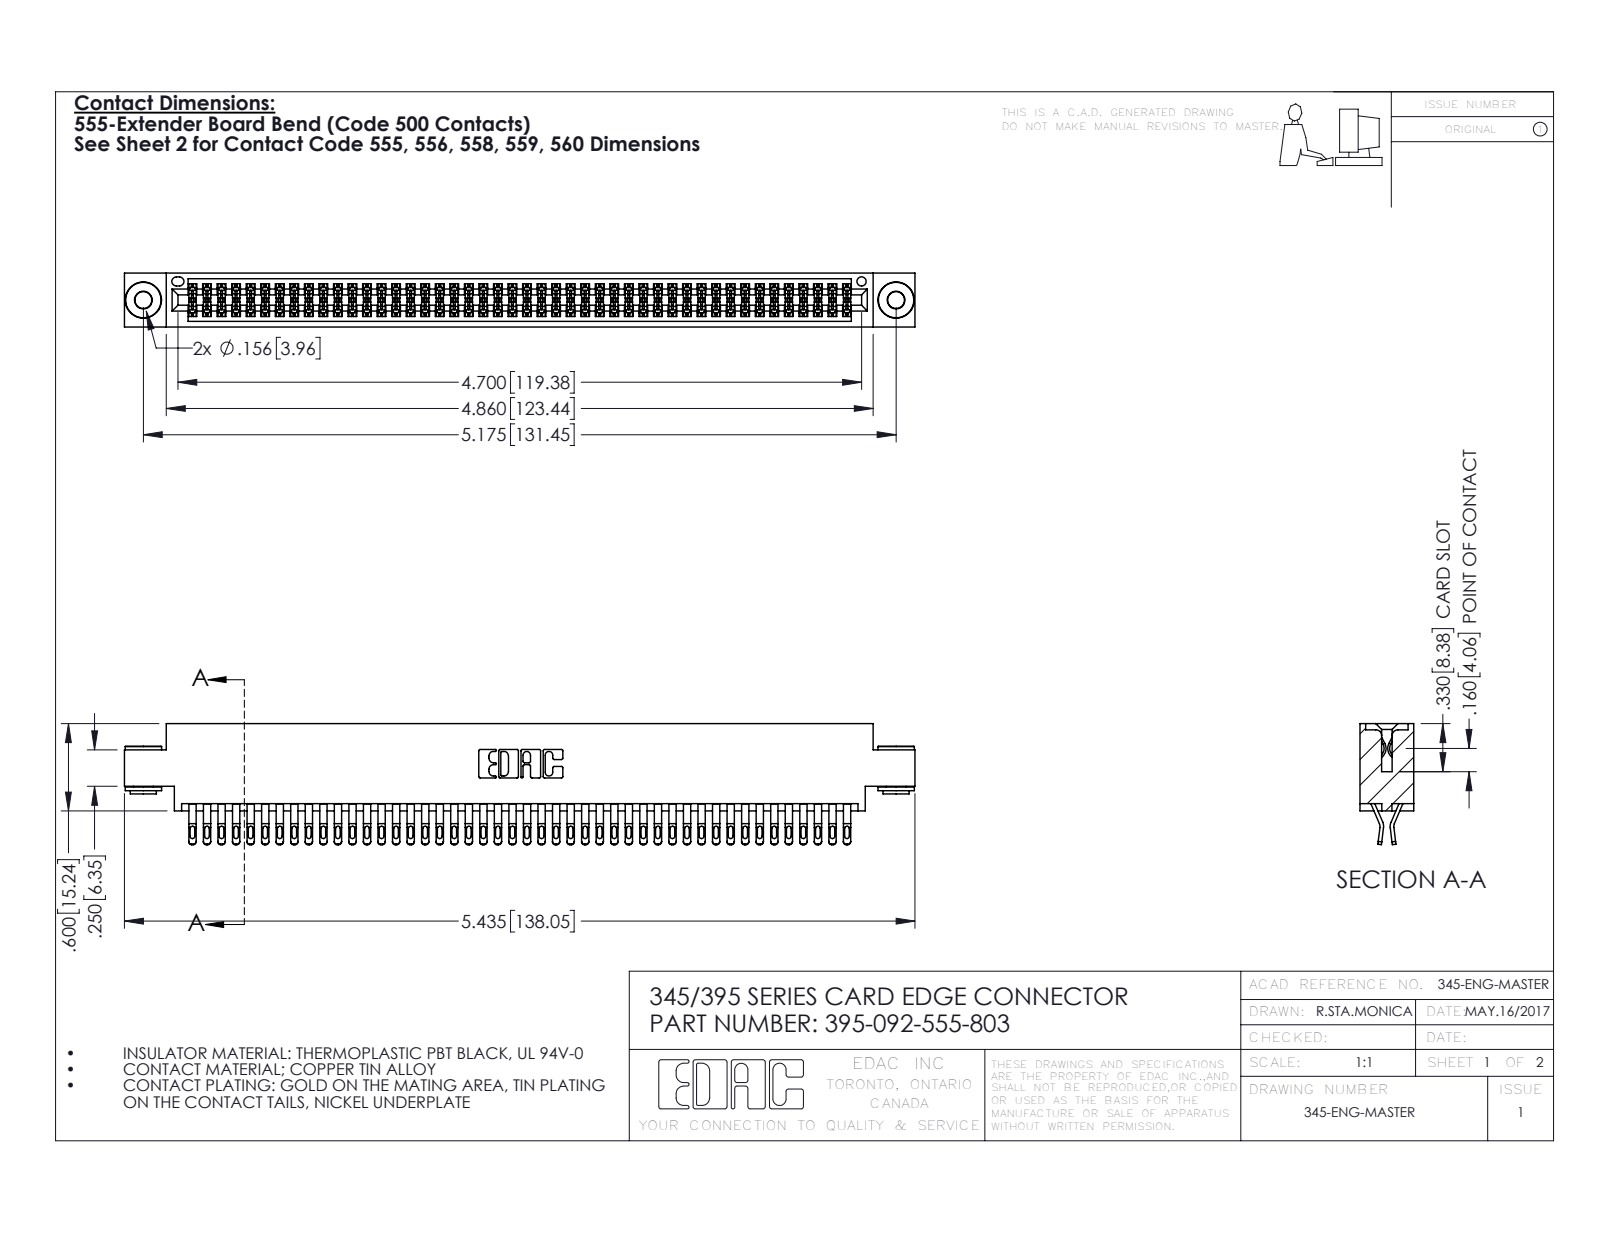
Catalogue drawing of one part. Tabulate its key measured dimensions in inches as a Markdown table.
| quantity | value |
| --- | --- |
| part name | 345-250-002_345-250-002-102; 345 Part_0.170 Offset - 0.156 Dia-TH; 345-292-001_555 Tail; 395-092-555-803 |
| STEP written by | SolidWorks 2016 (CONFIG_CONTROL_DESIGN) |
| units | inches |
| bodies | 95 solids, 5320 faces (2946 planar, 2366 cylindrical, 8 other) |
| overall size | 5.435 × 0.832 × 0.37 |
| volume | 0.831 in³ |
| surface area | 33.3 in² |
| round holes (diameter × count) | 0.116 × 2, 0.156 × 2, 0.064 × 1 |
| round bosses / shafts (diameter × count) | 0.25 × 2, 0.18 × 2, 0.136 × 2 |
| partial cylindrical surfaces (radius × count) | 0.016 × 230, 0.02 × 184, 0.006 × 138, 0.01 × 22, 0.007 × 6, 0.031 × 6, 0.026 × 3, 0.01 × 2 |
| main face-to-face distances | 0.072, 0.298, 0.37, 0.025, 0.2, 0.098, 0.272, 0.225, 0.175, 0.149 |
| hole center spacings | 0.27, 4.939, 5.175 |
